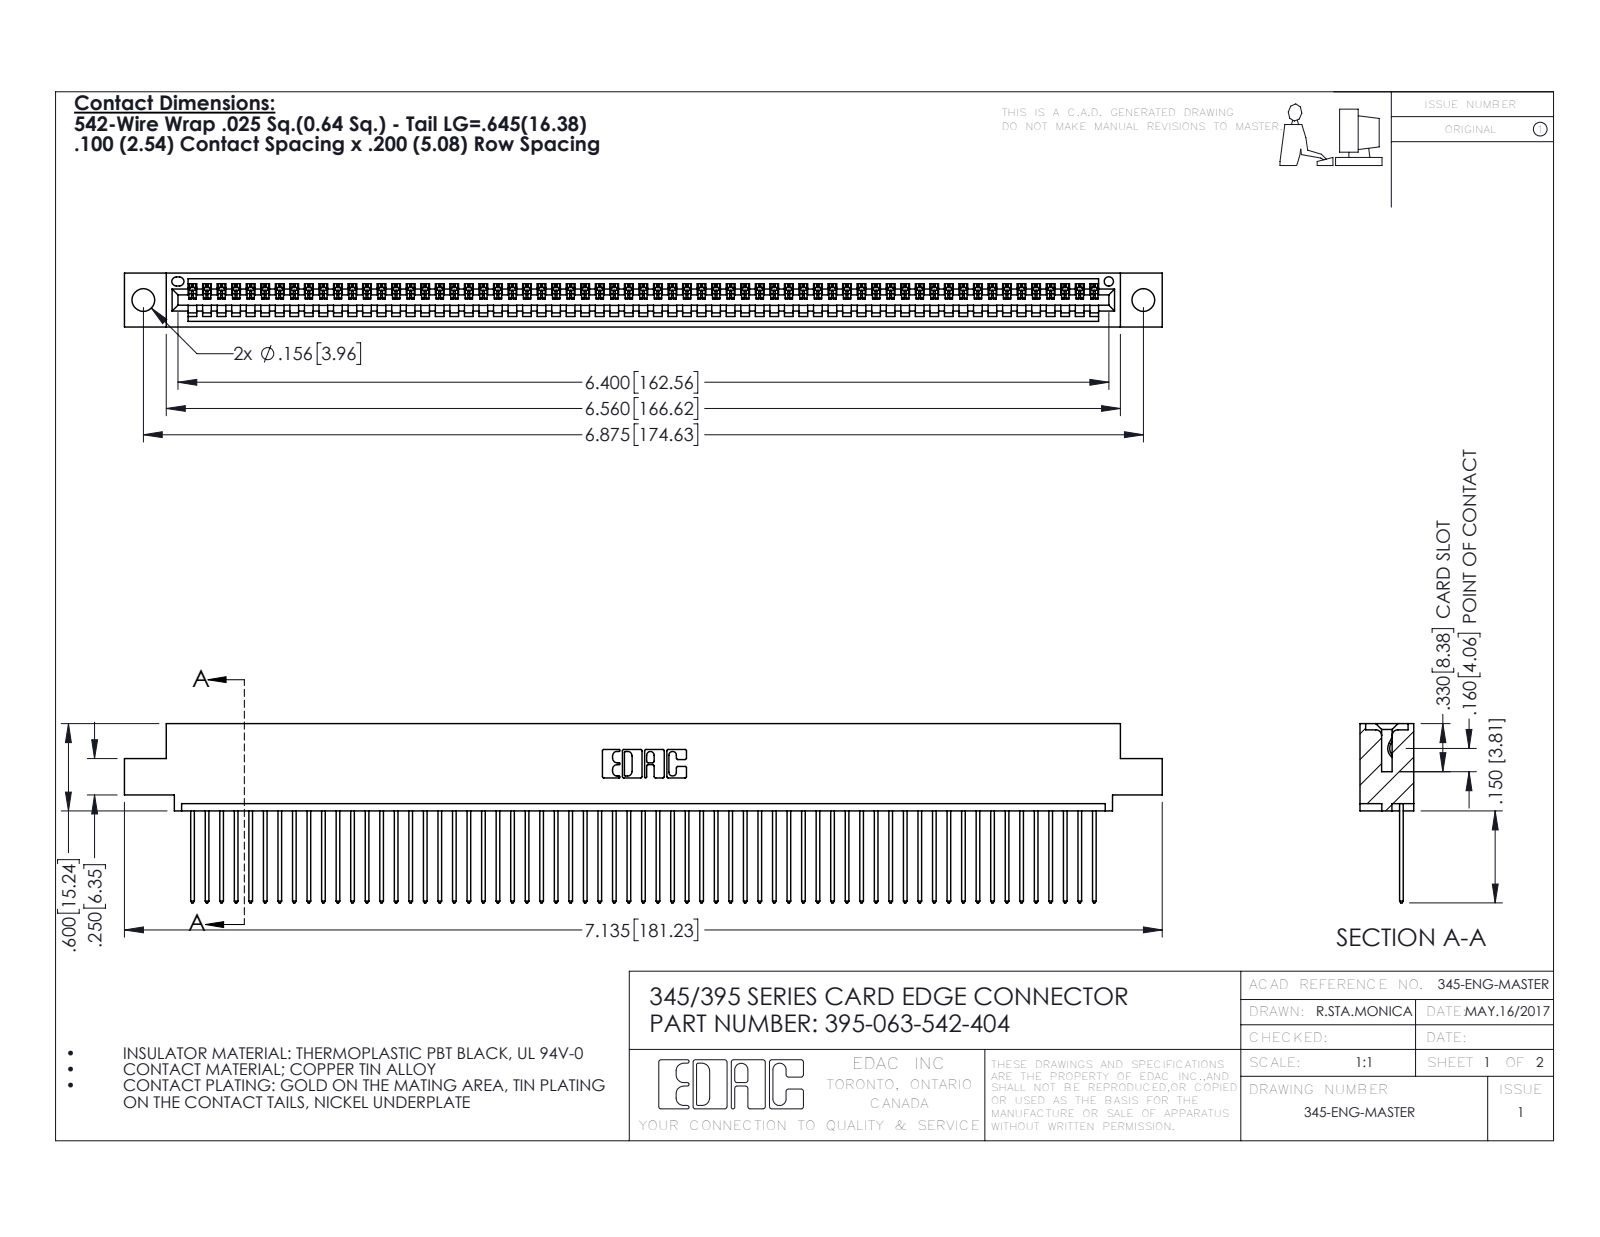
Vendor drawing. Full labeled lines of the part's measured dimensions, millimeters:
Part name (STEP PRODUCT): 345-292-001_345-293-142; 395-063-542-404; 345 Part_0.110 Offset - 0.156 Dia-TH
STEP written by: SolidWorks 2016 (CONFIG_CONTROL_DESIGN)
Units: millimetres
Bodies: 64 solids, 3784 faces (2604 planar, 1180 cylindrical, 0 other)
Overall size (bounding box): 181.2 × 31.3 × 9.4
Volume: 17 370 mm³ · Surface area: 24 140 mm²
Round holes (diameter × count): ⌀4 ×2, ⌀1.6 ×1
Partial cylindrical surfaces — rounded edges, fillets, slot ends (radius × count): R0.2 ×126, R0.3 ×126, R0.3 ×22, R0.2 ×6, R0.8 ×6, R0.7 ×3, R0.8 ×2, R1 ×2
Main face-to-face distances: 1.8, 7.6, 2.5, 6.9, 0.6, 9.4, 5.1, 5.7, 3.8, 1.8
Hole centre spacings: 6.9, 168.6, 174.6
